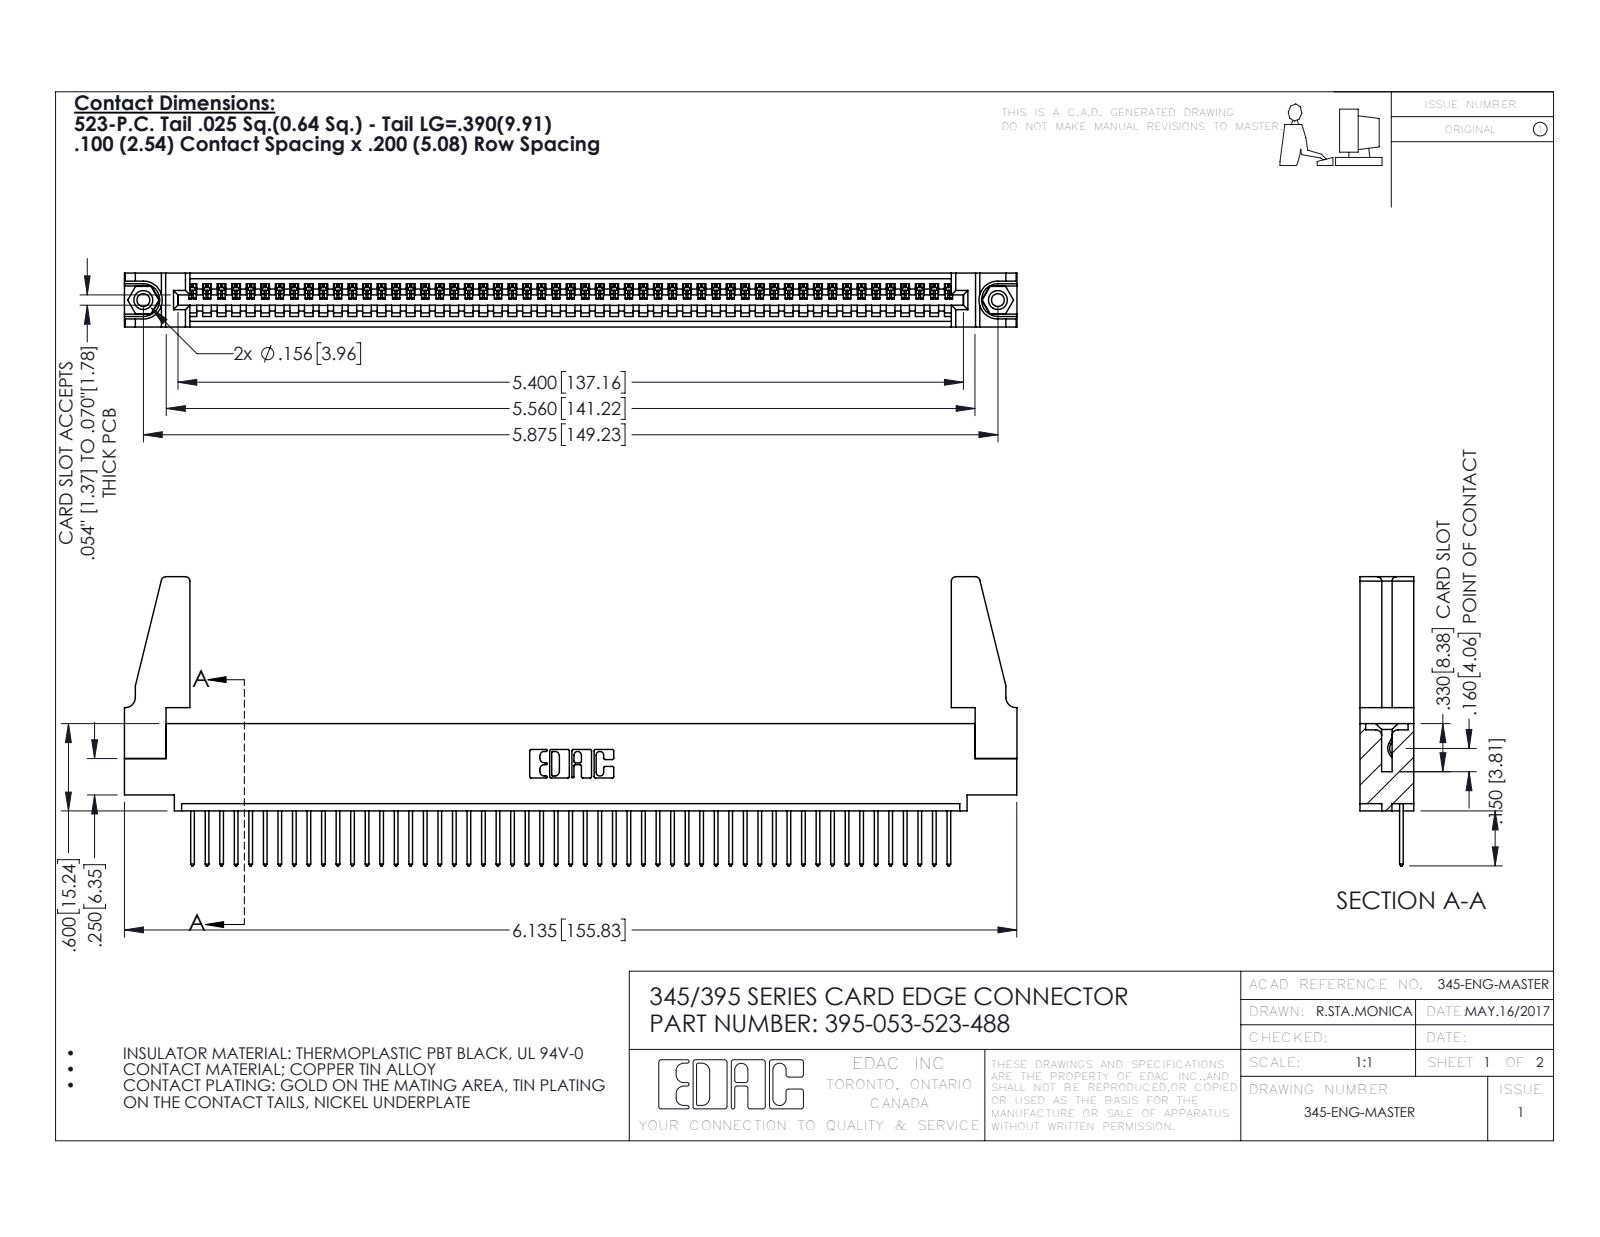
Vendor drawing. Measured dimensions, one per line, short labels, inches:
name: 395-053-523-488; 345-220-078_345-220-088; 345-250-001_345-250-001-102; 345-292-001_345-293-123 (+1 more)
written by: SolidWorks 2016 (CONFIG_CONTROL_DESIGN)
unit: in
bodies: 58 solids, 3328 faces (2276 planar, 1036 cylindrical, 16 other)
size: 6.136 × 1.987 × 0.37
volume: 1.102 in³; area: 35.78 in²
holes: 2× ⌀0.089, 2× ⌀0.125, 2× ⌀0.156, 1× ⌀0.064
bosses: 2× ⌀0.155
rounds: 106× R0.006, 106× R0.01, 22× R0.01, 8× R0.03, 6× R0.007, 6× R0.031, 3× R0.026, 2× R0.031
face distances: 0.072, 0.298, 0.37, 0.098, 0.272, 0.025, 0.2, 0.225, 0.149, 0.072
hole spacings: 0.27, 5.639, 5.875
